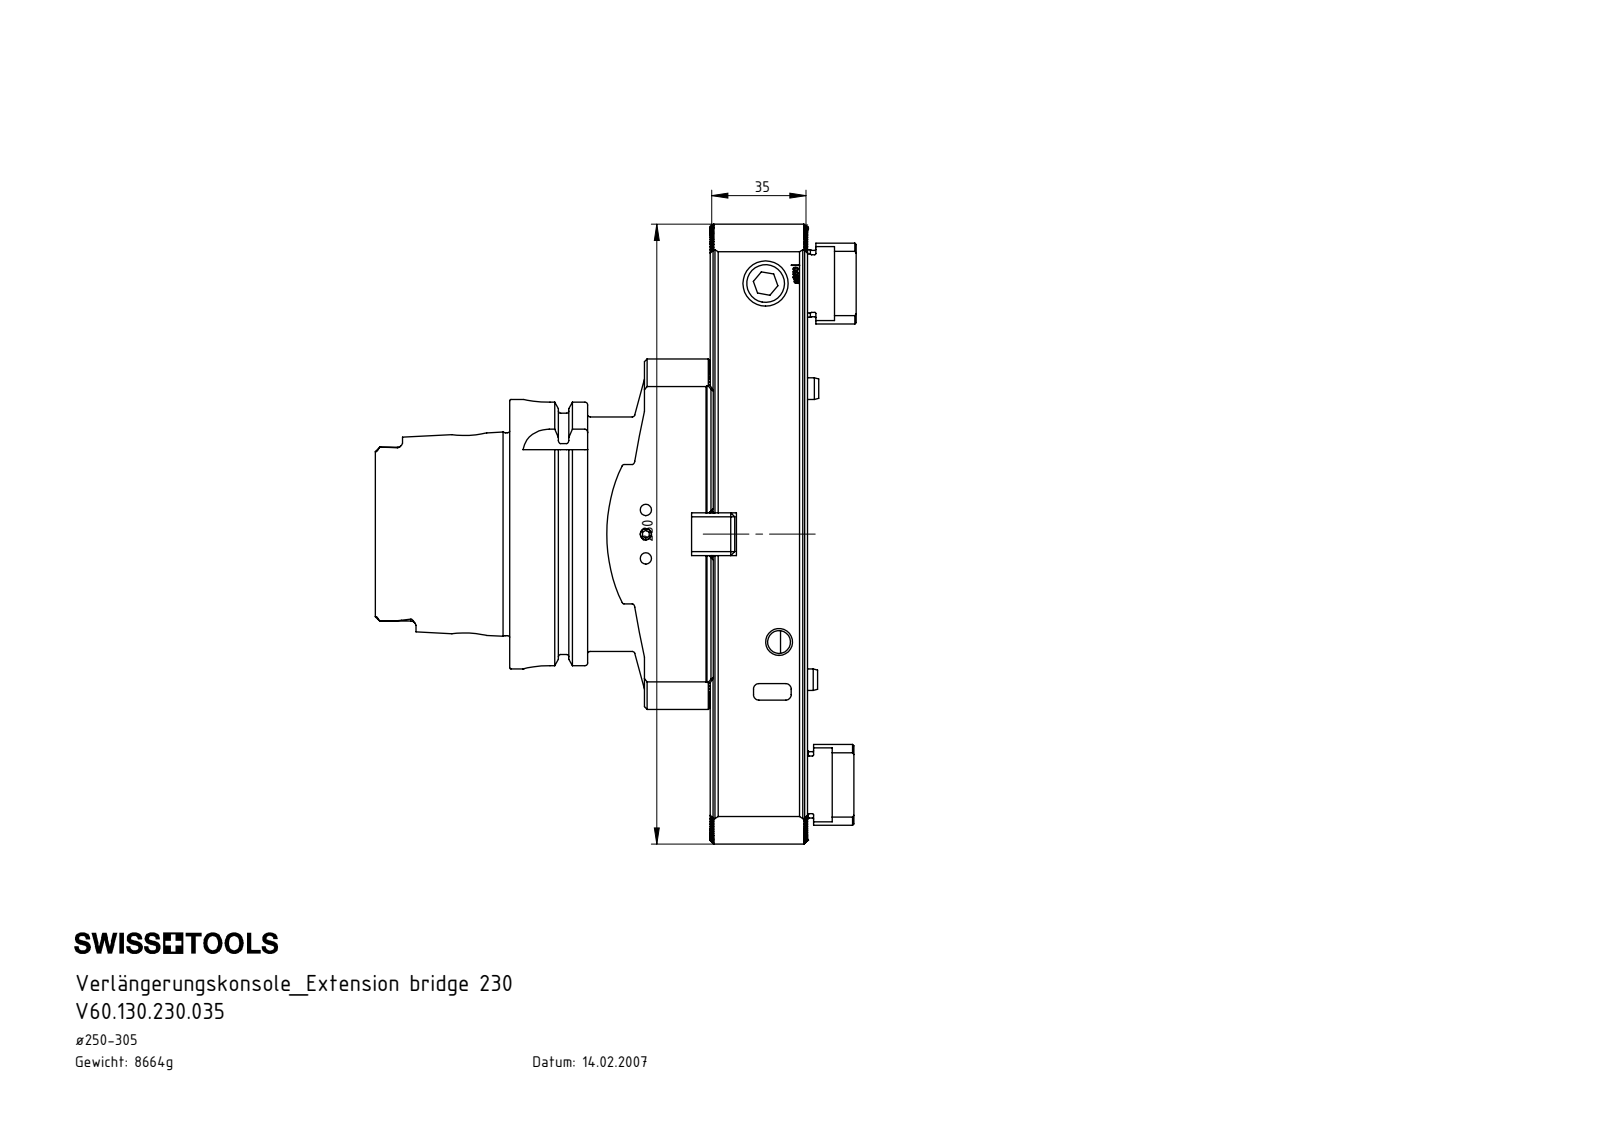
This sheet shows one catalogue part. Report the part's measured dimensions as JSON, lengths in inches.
{"part_name": "DIN 6912 - M10 x 12; VK1-ER3.001.028_A; VK1-ER2.101.010_A; VK1-ER7.001.012_mit kurzer Schraube (+8 more)", "step_written_by": "SolidWorks 2017 (AUTOMOTIVE_DESIGN)", "units": "inches", "bodies": {"solids": 27, "faces": 1503, "planar": 993, "cylindrical": 299, "other": 211}, "overall_size": [9.055, 3.74, 2.385], "volume_in3": 36.37, "surface_area_in2": 210.4, "round_holes": [[0.197, 4], [0.236, 4], [0.268, 4], [0.512, 4], [0.748, 4], [0.079, 2], [0.315, 2], [0.335, 2], [0.413, 2], [0.433, 2], [0.551, 2], [0.709, 2]], "round_bosses_or_shafts": [[0.63, 4], [0.236, 4], [0.394, 2], [0.315, 2]], "partial_cylinders_radius": [[0.006, 66], [0.079, 8], [0.236, 4], [0.484, 2], [0.591, 2], [2.559, 2], [0.313, 1]], "face_to_face_distances": [2.756, 0.472, 3.228, 0.068, 0.02, 3.248, 0.655, 0.453, 2.776, 3.701], "hole_center_spacings": [7.323, 0.311, 0.73, 0.772, 0.828, 1.359, 1.378, 1.381]}
